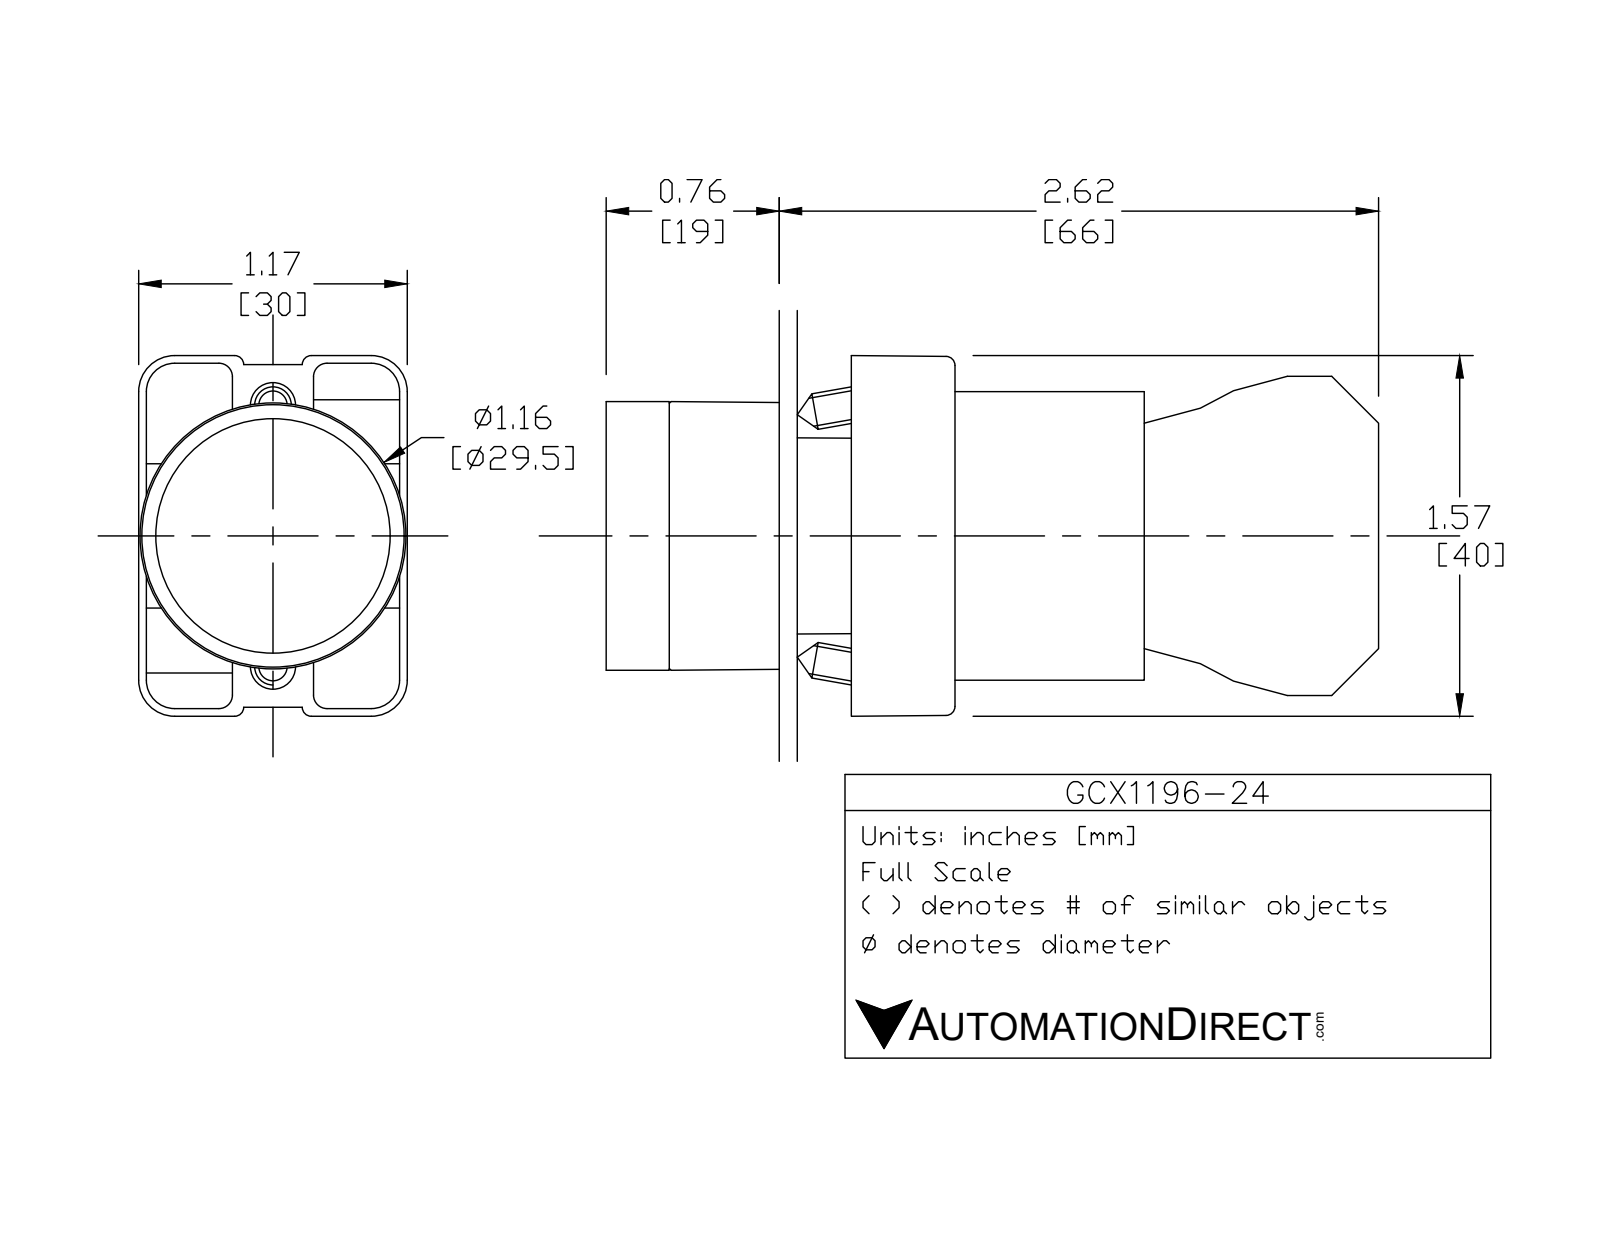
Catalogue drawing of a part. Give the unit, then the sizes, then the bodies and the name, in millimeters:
Units: millimetres
Overall size (bounding box): 84.3 × 40.2 × 29.9
Round holes (diameter × count): ⌀2 ×2, ⌀3.1 ×2, ⌀3.3 ×2, ⌀2.2 ×1, ⌀5 ×1, ⌀11.9 ×1, ⌀22.3 ×1, ⌀22.6 ×1, ⌀26 ×1
Round bosses / shafts (diameter × count): ⌀4 ×4, ⌀29.8 ×1, ⌀25.5 ×1, ⌀24 ×1, ⌀21.7 ×1, ⌀19.8 ×1, ⌀12.8 ×1
Partial cylindrical surfaces — rounded edges, fillets, slot ends (radius × count): R1.5 ×24, R1 ×12, R3.1 ×12, R4 ×12, R1 ×8, R3.3 ×2, R0.5 ×1, R1.6 ×1
Main face-to-face distances: 21, 51.3, 30.3, 14.7, 29.7, 0.8, 7, 0.8, 19, 14.6
Hole centre spacings: 6, 13.8, 12, 12.4
Volume: 45 790 mm³ · Surface area: 25 000 mm²
Bodies: 8 solids, 431 faces (252 planar, 148 cylindrical, 31 other)
Part name (STEP PRODUCT): ECX1050; ecx1040; ecx1029; GCX1196-24 (+1 more)
STEP written by: SolidWorks 2016 (AUTOMOTIVE_DESIGN)
